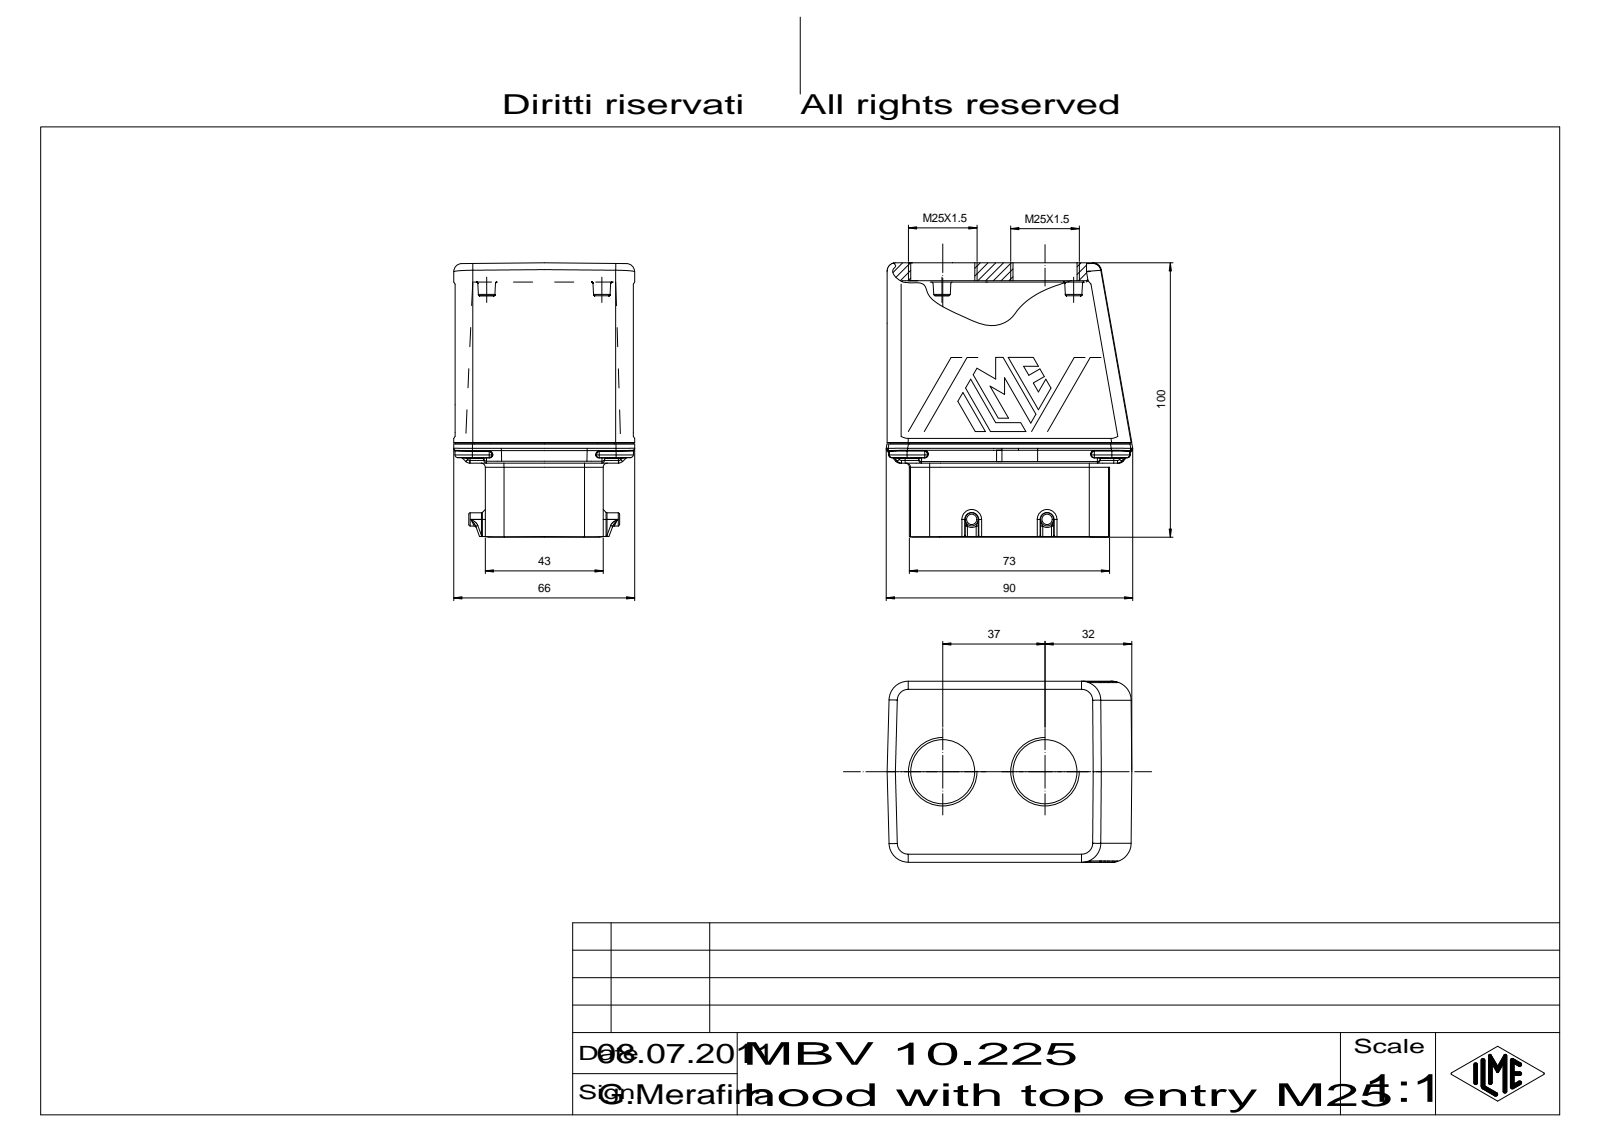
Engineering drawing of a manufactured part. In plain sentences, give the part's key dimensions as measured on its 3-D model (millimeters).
The part is named "53848_Body_1_Body_1.1". Its 3-D file was written by "CoCreate Modeling 16.00A 16-Aug-2008 (C) Parametric Technology GmbH (AUTOMOTIVE_DESIGN)". It is 1 solid with 612 faces: 298 planar, 150 cylindrical and 164 other. Overall it measures 99.49 by 88.76 by 66.01 millimeters. Its volume is 384 816 cubic millimeters and its surface area 47 706 square millimeters. Round holes: 2 of diameter 25. Round bosses or shafts: 2 of diameter 4.8. Partial cylindrical surfaces (rounded edges, fillets, slot ends): 46 of radius 1, 18 of radius 0.3, 12 of radius 7, 10 of radius 3, 8 of radius 0.5, 6 of radius 1.5, 4 of radius 4.2, 4 of radius 5. The main face-to-face distances are 72.73, 65.01, 0.4, 65.41, 11, 54.01, 54, 43, 11.01, 11.4. The hole center spacings are 37.3.
